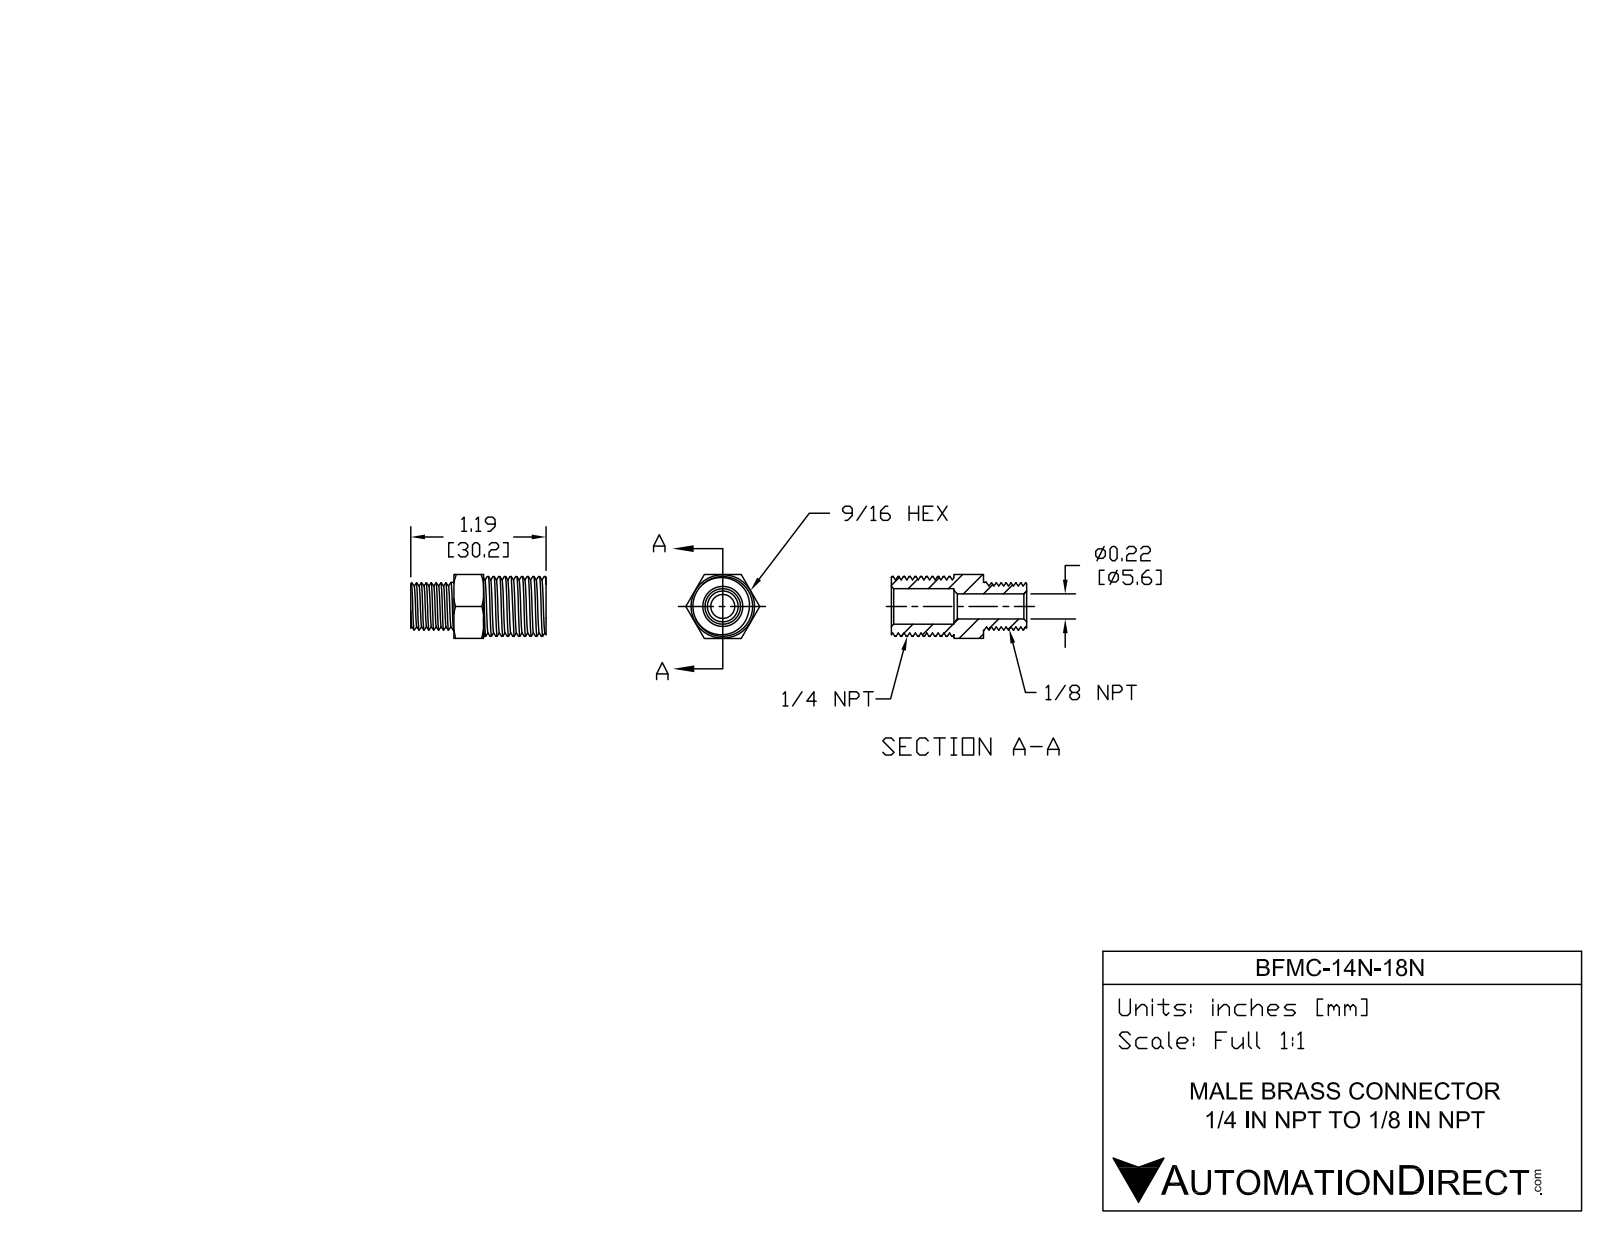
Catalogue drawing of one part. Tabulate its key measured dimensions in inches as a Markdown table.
| quantity | value |
| --- | --- |
| part name | BFMC-14N-18N |
| STEP written by | SolidWorks 2015 (CONFIG_CONTROL_DESIGN) |
| units | inches |
| bodies | 1 solid, 76 faces (12 planar, 28 cylindrical, 36 other) |
| overall size | 1.189 × 0.618 × 0.535 |
| volume | 0.153 in³ |
| surface area | 3.968 in² |
| round holes (diameter × count) | 0.211 × 1, 0.312 × 1 |
| round bosses / shafts (diameter × count) | 0.525 × 1 |
| main face-to-face distances | 0.535, 0.81, 1.189, 0.379, 0.55, 0.26, 0.639, 0.267 |
